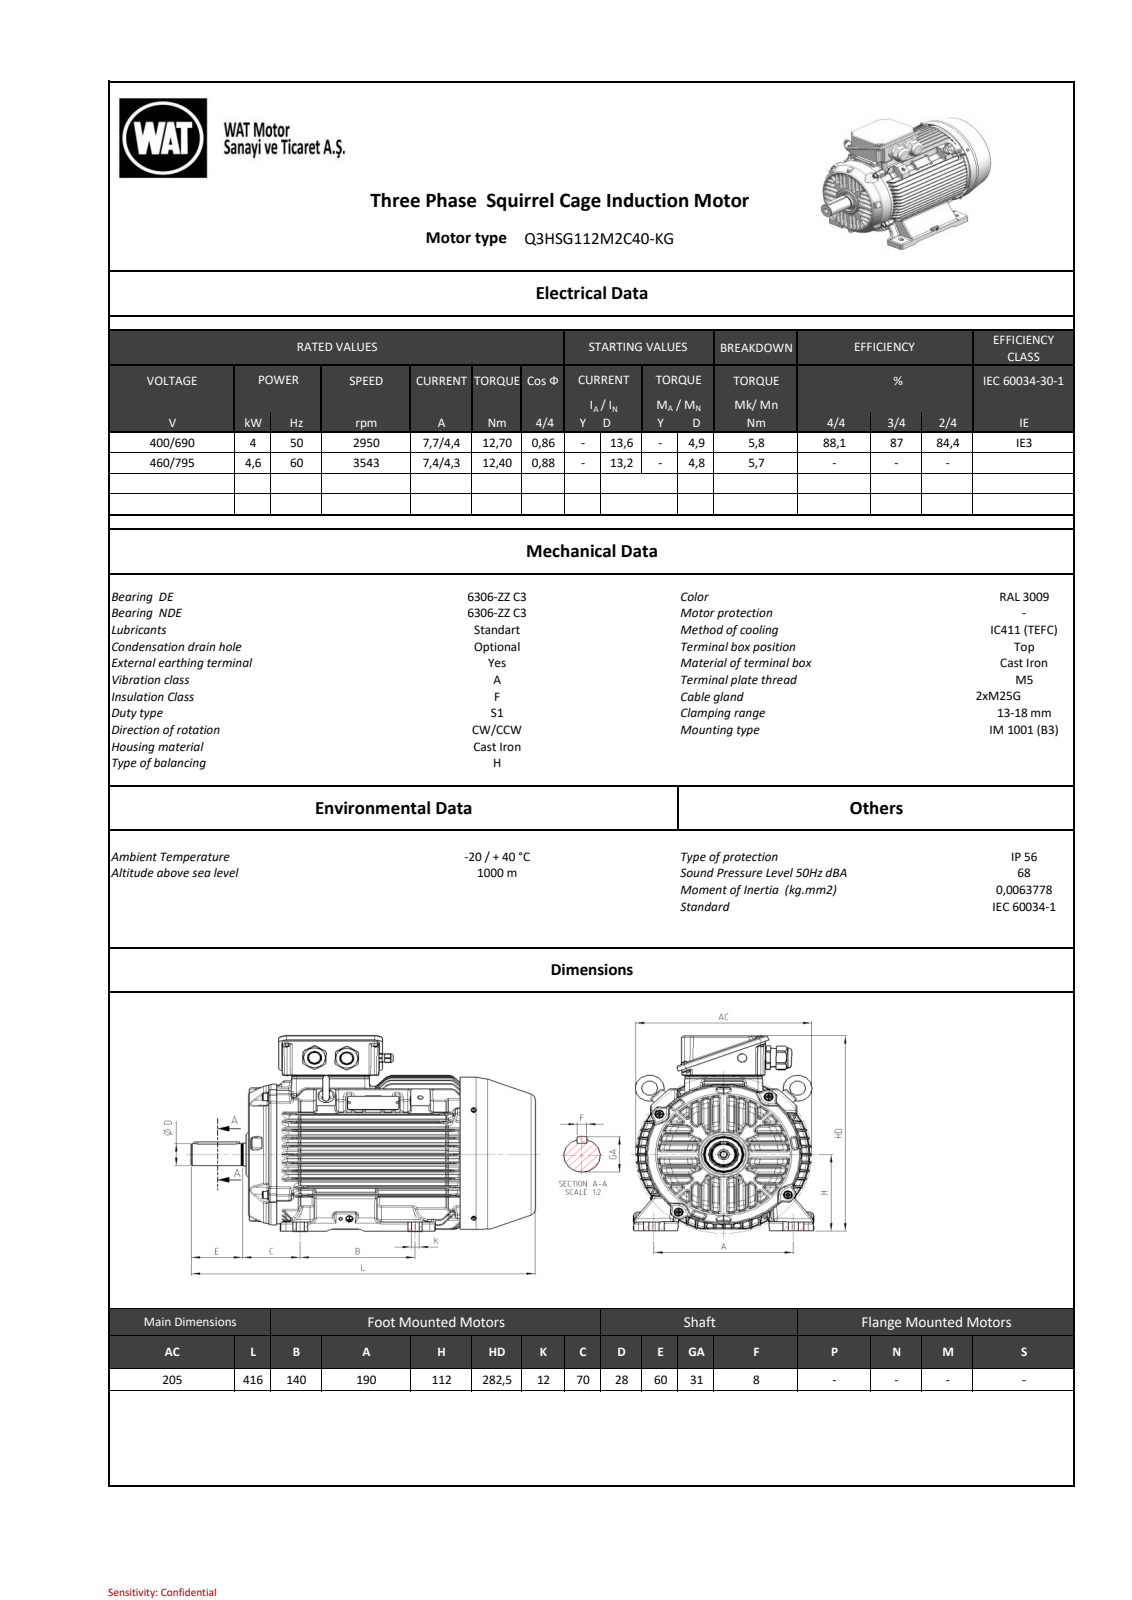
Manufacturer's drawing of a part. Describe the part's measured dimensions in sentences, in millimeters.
The part is named "260037F440EAov6a". Its 3-D file was written by "SIEMENS PLM Software NX 11.0 (AUTOMOTIVE_DESIGN)". It is 0 solids with 5258 faces: 965 planar, 1366 cylindrical and 2927 other. Overall it measures 416 by 282.48 by 247.6 millimeters. Round holes: 7 of diameter 5, 4 of diameter 2.5, 2 of diameter 3.2, 2 of diameter 6.8, 1 of diameter 4.2, 1 of diameter 6.5, 1 of diameter 6.6, 1 of diameter 8.5, 1 of diameter 10, 1 of diameter 10.5, 1 of diameter 43.4, 1 of diameter 43.6. Round bosses or shafts: 8 of diameter 10, 4 of diameter 12, 4 of diameter 8.65, 4 of diameter 8, 4 of diameter 4, 2 of diameter 31.6, 2 of diameter 20, 1 of diameter 200. Partial cylindrical surfaces (rounded edges, fillets, slot ends): 279 of radius 4, 169 of radius 3, 98 of radius 1.5, 61 of radius 2, 36 of radius 1, 30 of radius 1.8, 30 of radius 5, 28 of radius 6. The main face-to-face distances are 13.53, 13.62, 27.15, 40.84, 27.31, 13.69, 78.83, 65.21, 51.68, 13.78. The hole center spacings are 89.5, 126.57, 31.07, 102.68, 146.62, 176.28, 179, 27.5.
